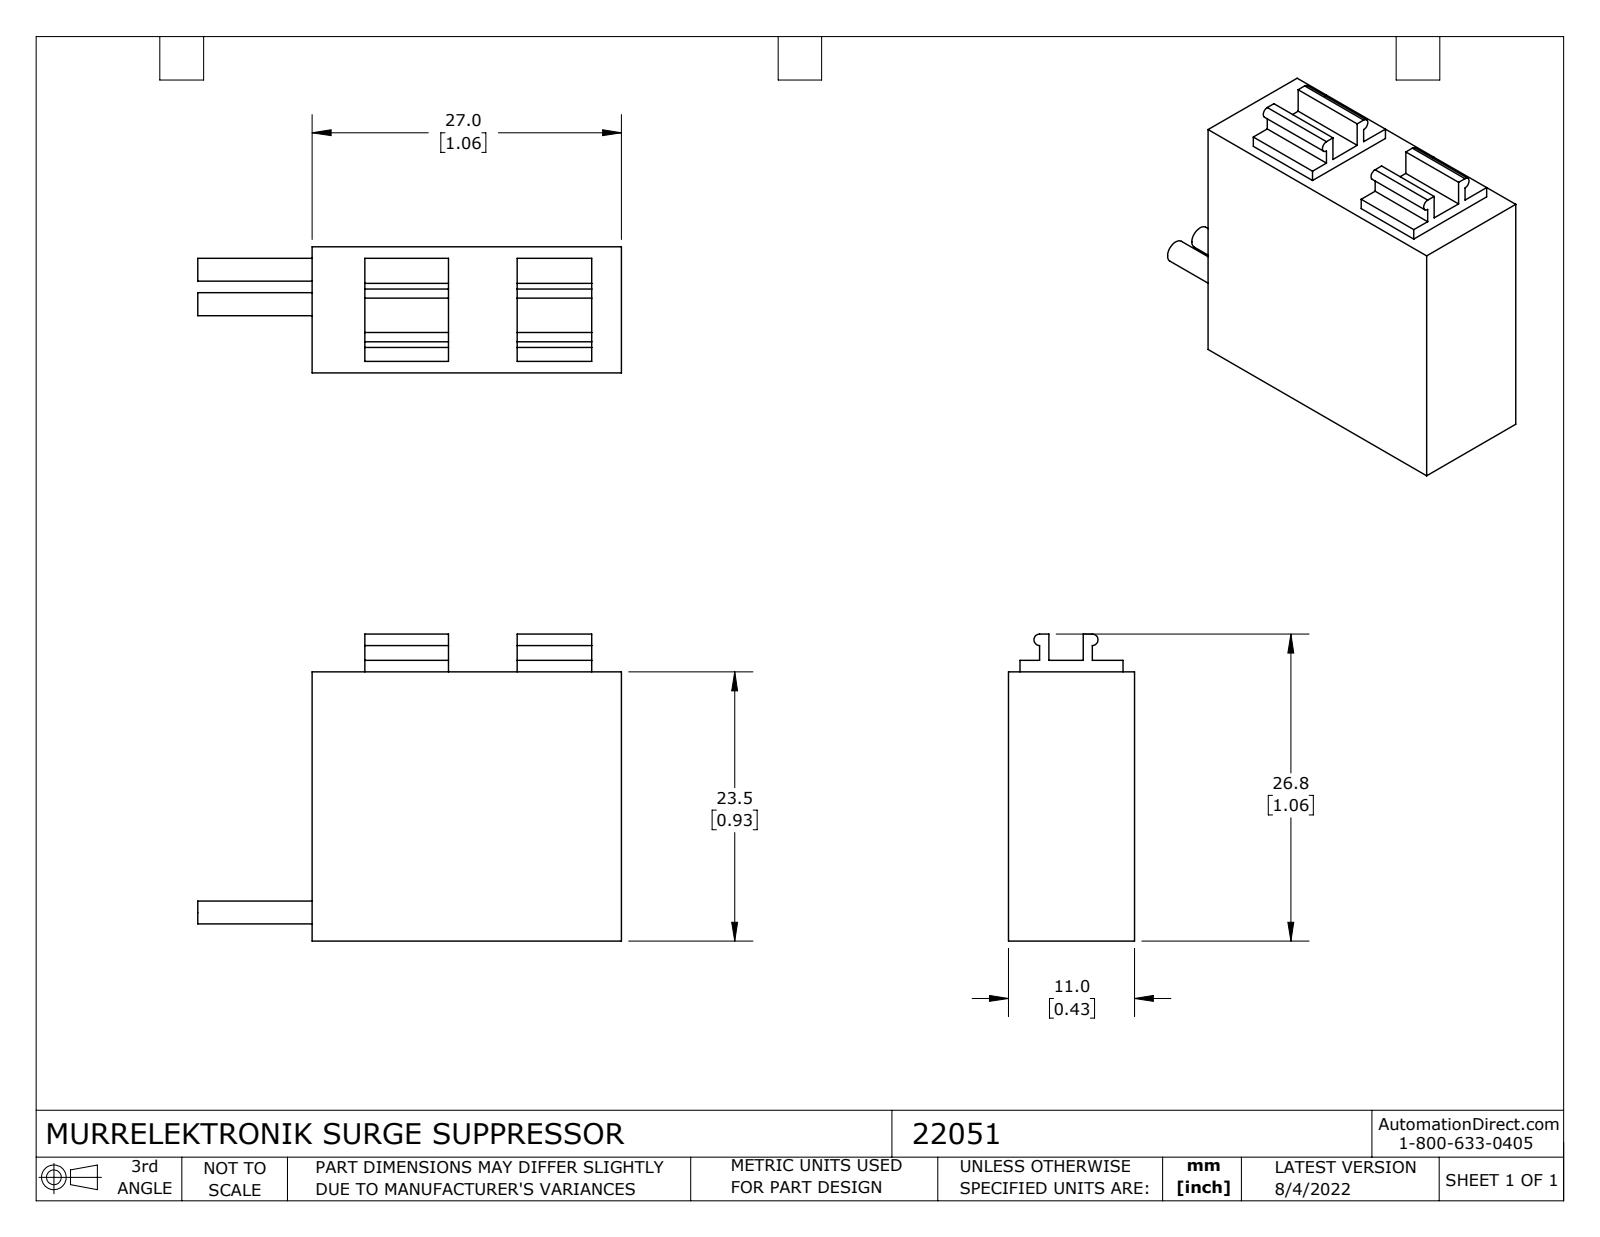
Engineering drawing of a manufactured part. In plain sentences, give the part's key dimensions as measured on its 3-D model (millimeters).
The part is named "22051". Its 3-D file was written by "SolidWorks 2021 (CONFIG_CONTROL_DESIGN)". It is 1 solid with 43 faces: 34 planar, 9 cylindrical and 0 other. Overall it measures 37 by 26.8 by 11 millimeters. Its volume is 7 228 cubic millimeters and its surface area 2 730 square millimeters. Round bosses or shafts: 2 of diameter 2. Partial cylindrical surfaces (rounded edges, fillets, slot ends): 2 of radius 0.5. The main face-to-face distances are 11, 27, 23.5, 1, 24.5, 0.8, 3.8, 10, 4.48, 7.48.
